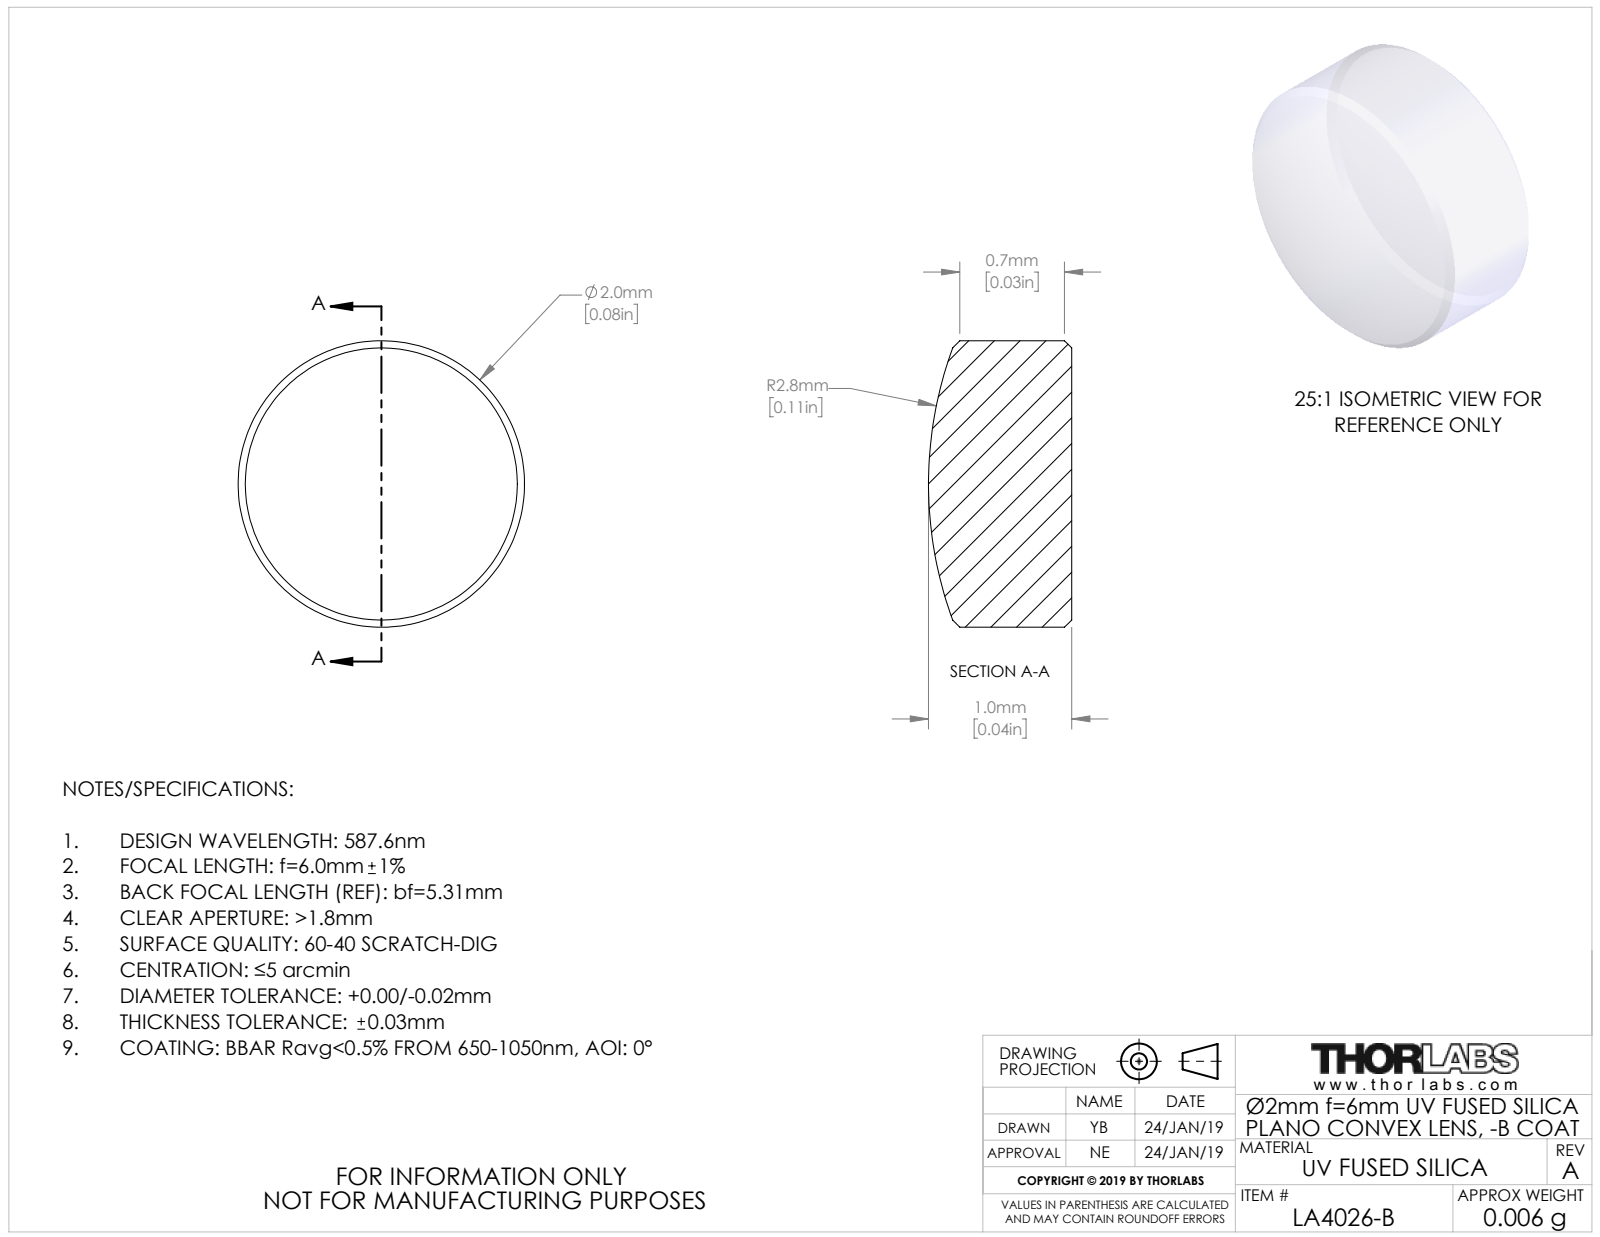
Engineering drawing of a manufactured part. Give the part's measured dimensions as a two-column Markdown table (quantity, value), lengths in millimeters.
| quantity | value |
| --- | --- |
| part name | TTN162815-E0W |
| STEP written by | SolidWorks 2018 (CONFIG_CONTROL_DESIGN) |
| units | millimeters |
| bodies | 1 solid, 9 faces (1 planar, 2 cylindrical, 6 other) |
| overall size | 2 × 2 × 1 |
| volume | 3 mm³ |
| surface area | 11 mm² |
| round bosses / shafts (diameter × count) | 2 × 1 |
